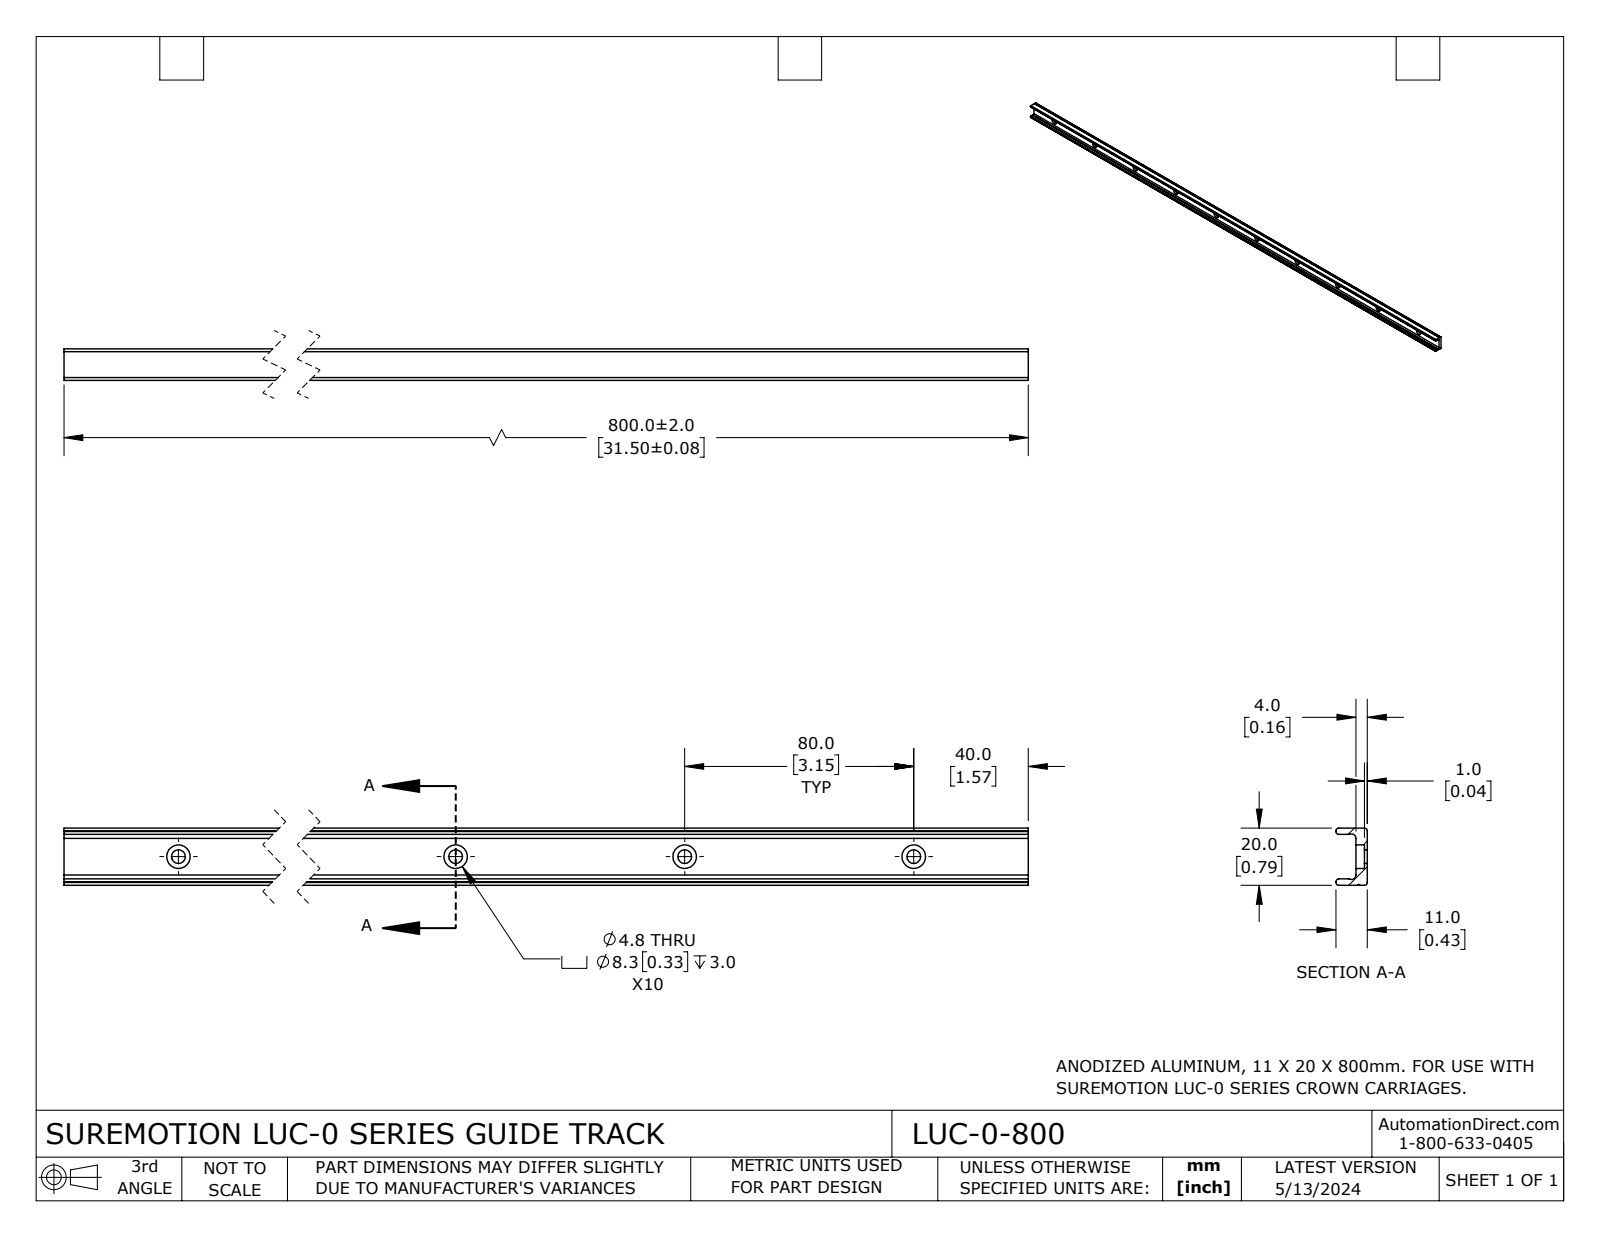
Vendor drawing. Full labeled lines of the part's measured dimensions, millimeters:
Part name (STEP PRODUCT): LUC-0-800
STEP written by: SolidWorks 2023 (CONFIG_CONTROL_DESIGN)
Units: millimetres
Bodies: 1 solid, 72 faces (21 planar, 51 cylindrical, 0 other)
Overall size (bounding box): 800 × 19.99 × 11
Volume: 86 290 mm³ · Surface area: 59 071 mm²
Round holes (diameter × count): ⌀4.8 ×10, ⌀8.25 ×5, ⌀8.26 ×5
Partial cylindrical surfaces — rounded edges, fillets, slot ends (radius × count): R0.99 ×8, R1.6 ×2, R0.33 ×1
Main face-to-face distances: 4.01, 20, 2.23, 17.77, 15.54, 11, 6.99, 1.01, 3, 9.99
Hole centre spacings: 80, 160, 240, 320, 400, 480, 560, 640
